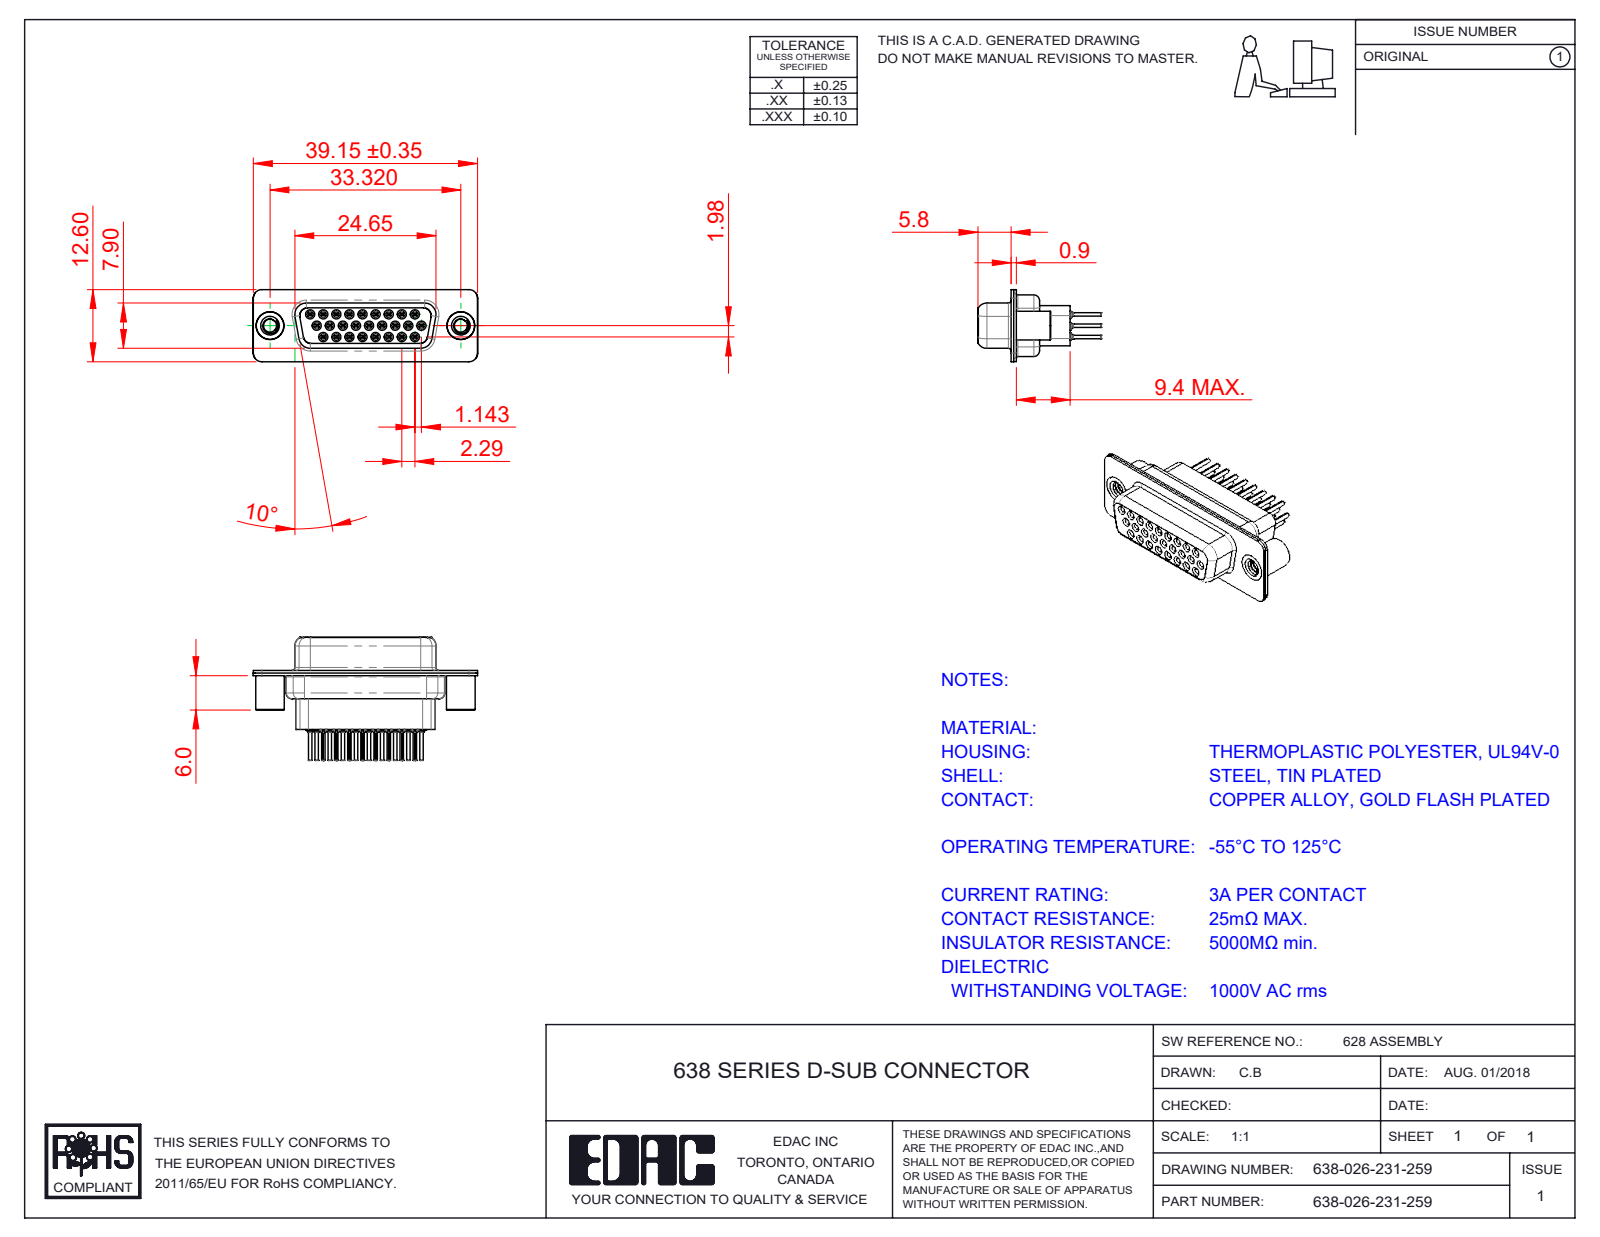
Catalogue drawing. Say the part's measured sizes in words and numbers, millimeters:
The part is named "638 Contact Row 2_31; 638 Shell Rear_26 Contacts; 638 Shell Front_26 Contacts; 638-026-231-259 (+4 more)". Its 3-D file was written by "SolidWorks 2020 (CONFIG_CONTROL_DESIGN)". It is 31 solids with 3499 faces: 873 planar, 1015 cylindrical and 1611 other. Overall it measures 39.19 by 21.5 by 12.6 millimeters. Its volume is 2 772 cubic millimeters and its surface area 10 061 square millimeters. Round holes: 26 of diameter 0.2, 26 of diameter 0.8, 26 of diameter 1, 26 of diameter 1.1, 26 of diameter 1.6, 26 of diameter 1.7, 26 of diameter 1.8, 2 of diameter 2.26, 2 of diameter 4, 2 of diameter 4.05, 2 of diameter 4.85. Round bosses or shafts: 26 of diameter 2, 26 of diameter 1.5, 26 of diameter 1.2, 26 of diameter 0.6, 2 of diameter 5, 2 of diameter 4.95, 2 of diameter 4.8. Partial cylindrical surfaces (rounded edges, fillets, slot ends): 52 of radius 0.1, 20 of radius 1.5, 18 of radius 0.28, 12 of radius 2, 8 of radius 1.55, 5 of radius 1.35, 4 of radius 0.25, 4 of radius 0.5. The main face-to-face distances are 0.45, 0.4, 6.6, 1.43, 8.88, 0.9, 7, 2.28, 5.8, 6.2. The hole center spacings are 3.96, 2.28, 4.57, 6.05, 2.29, 8.24, 6.86, 10.48.
